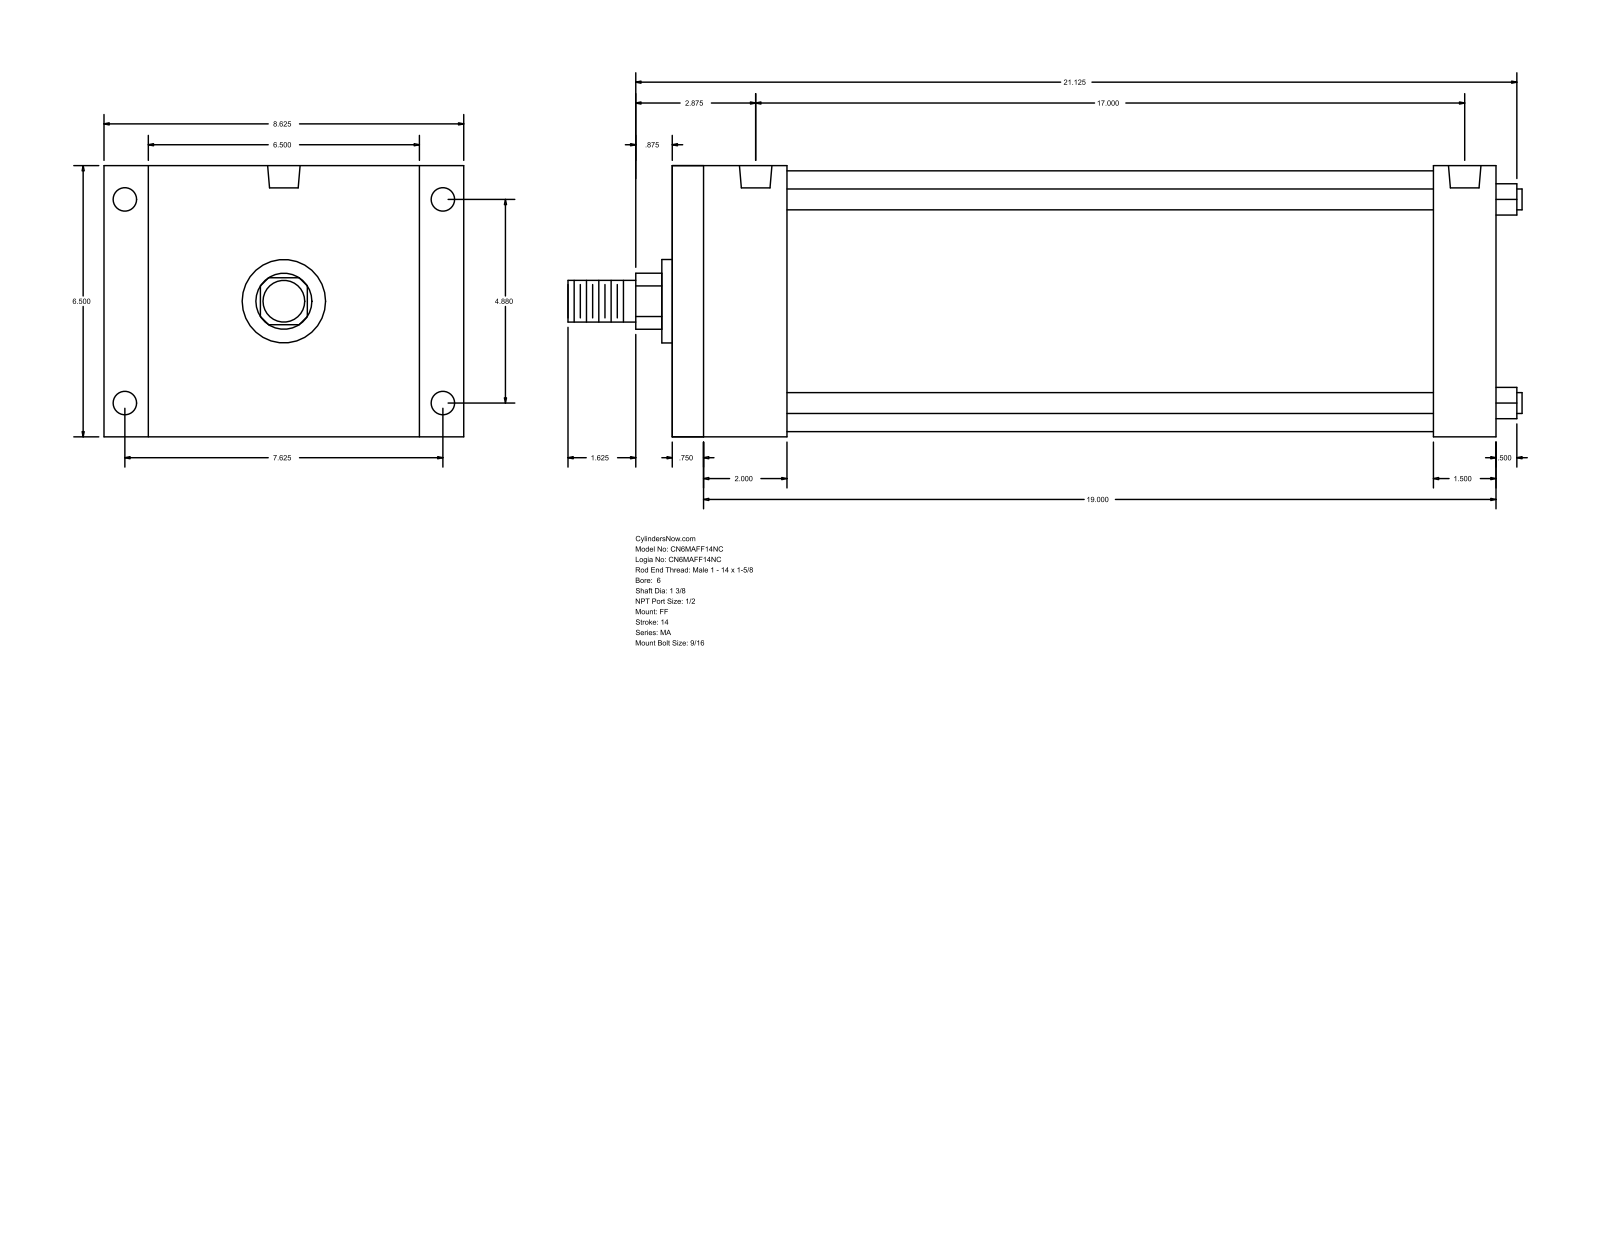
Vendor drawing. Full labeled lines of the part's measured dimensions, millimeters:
Part name (STEP PRODUCT): MA_FF__0600_1.375
STEP written by: GSSL Pune (CONFIG_CONTROL_DESIGN)
Units: millimetres
Bodies: 0 solids, 92 faces (64 planar, 28 cylindrical, 0 other)
Overall size (bounding box): 581.02 × 219.07 × 165.1
Round holes (diameter × count): ⌀14.29 ×4, ⌀17.46 ×4, ⌀19.77 ×2
Round bosses / shafts (diameter × count): ⌀12.7 ×4, ⌀158.75 ×1, ⌀50.8 ×1, ⌀34.92 ×1, ⌀25.4 ×1
Partial cylindrical surfaces — rounded edges, fillets, slot ends (radius × count): R17.06 ×1
Main face-to-face distances: 165.1, 501.65, 15.87, 485.78, 66.67, 50.8, 434.98, 463.54, 447.67, 396.87
Hole centre spacings: 123.96, 193.68, 229.95, 434.97, 3.18, 431.79
